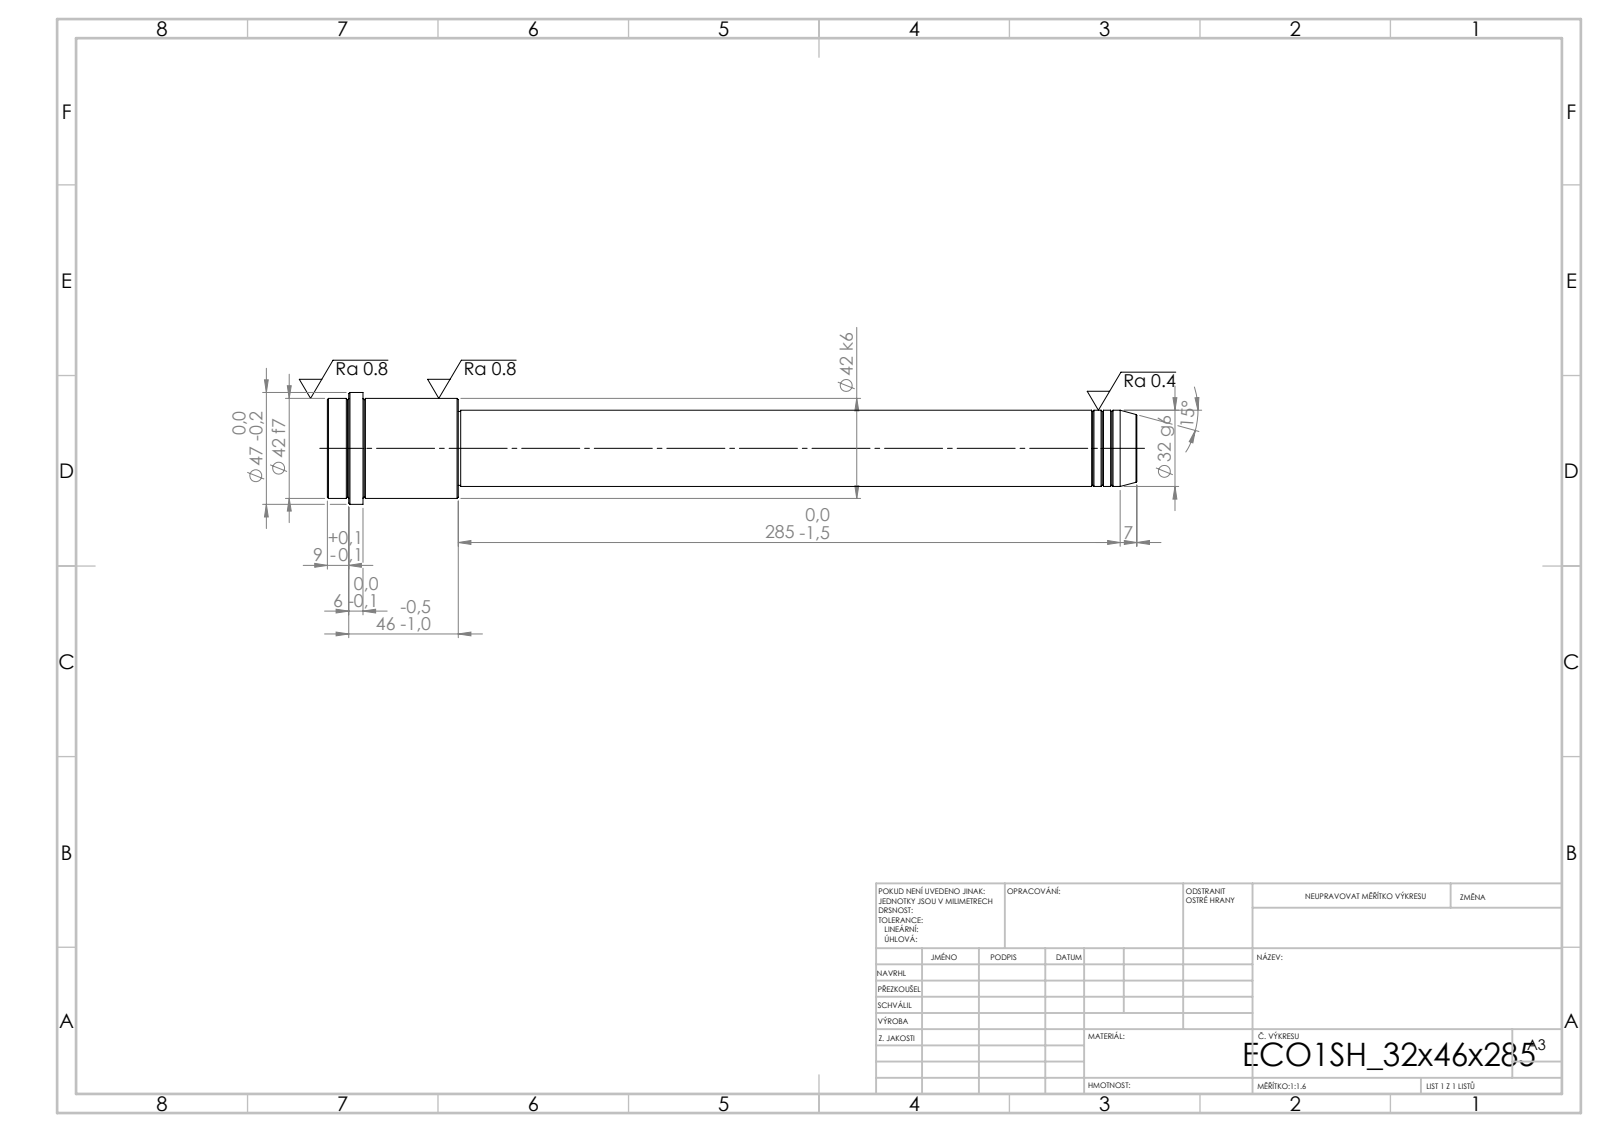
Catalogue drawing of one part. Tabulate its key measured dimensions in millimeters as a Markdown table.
| quantity | value |
| --- | --- |
| STEP written by | SolidWorks 2019 (CONFIG_CONTROL_DESIGN) |
| units | millimeters |
| bodies | 1 solid, 52 faces (6 planar, 16 cylindrical, 30 other) |
| overall size | 340 × 47 × 47 |
| volume | 306 550 mm³ |
| surface area | 39 548 mm² |
| round bosses / shafts (diameter × count) | 47 × 1, 42 × 1, 32 × 1, 31 × 1 |
| main face-to-face distances | 340, 285, 55, 325, 40, 15, 331, 46, 6, 9 |
